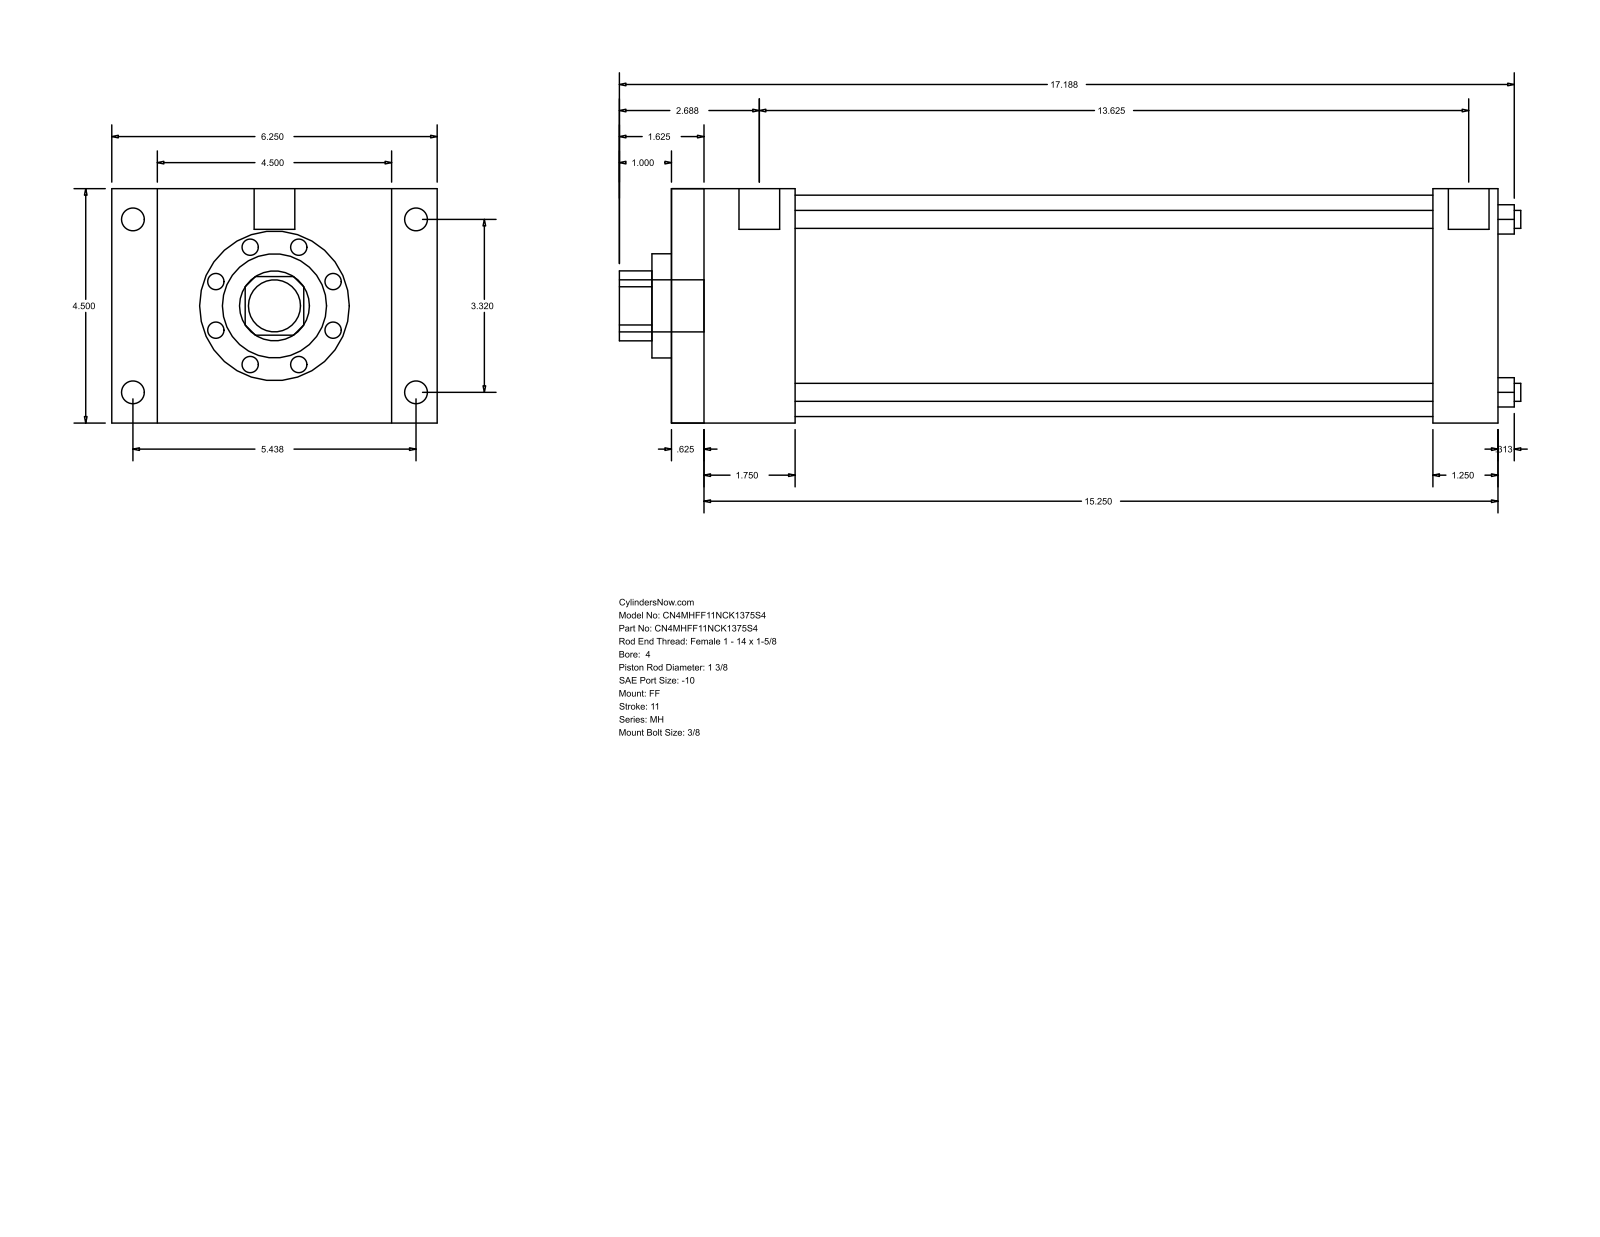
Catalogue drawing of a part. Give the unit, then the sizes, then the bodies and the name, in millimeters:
Units: millimetres
Overall size (bounding box): 439.74 × 158.75 × 114.3
Round holes (diameter × count): ⌀8.76 ×4, ⌀34.92 ×1, ⌀50.8 ×1, ⌀107.95 ×1
Round bosses / shafts (diameter × count): ⌀11.13 ×4, ⌀8.73 ×4, ⌀19.84 ×2, ⌀25.4 ×1
Partial cylindrical surfaces — rounded edges, fillets, slot ends (radius × count): R17.06 ×1
Main face-to-face distances: 114.3, 403.22, 15.87, 387.35, 60.32, 44.45, 342.9, 371.48, 355.61, 311.16
Hole centre spacings: 59.62, 84.32, 119.25
Bodies: 0 solids, 92 faces (64 planar, 28 cylindrical, 0 other)
Part name (STEP PRODUCT): MH_FF__0400_1.375
STEP written by: GSSL Pune (CONFIG_CONTROL_DESIGN)
